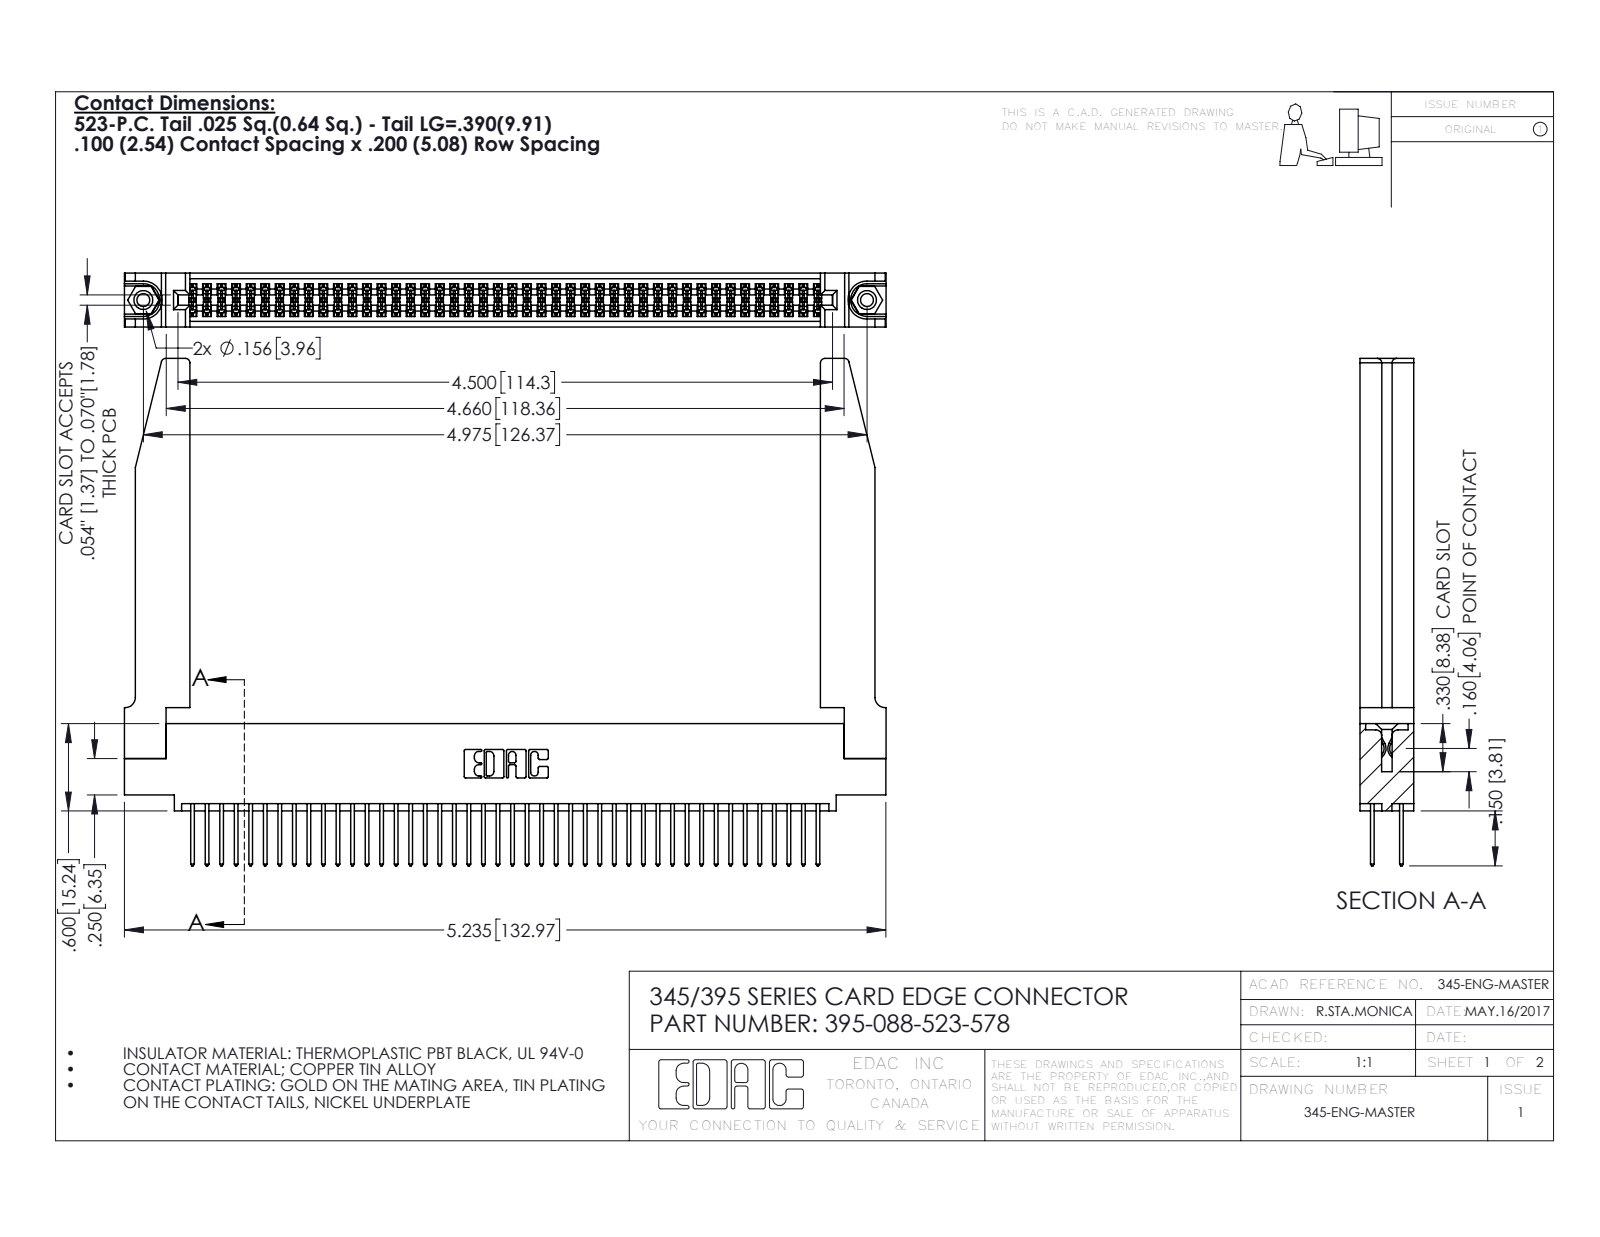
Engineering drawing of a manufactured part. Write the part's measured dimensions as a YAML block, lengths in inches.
part_name: "345-250-001_345-250-001-102; 345-220-078_345-220-078; 345-292-001_345-293-123; 345 Part_0.110 Offset - 0.156 Dia-TH (+1 more)"
step_written_by: "SolidWorks 2016 (CONFIG_CONTROL_DESIGN)"
units: inches
bodies: {solids: 93, faces: 4764, planar: 3130, cylindrical: 1582, other: 52}
overall_size: [5.236, 3.487, 0.37]
volume: 1.27
surface_area: 41.95
round_holes:
  - {diameter: 0.089, count: 2}
  - {diameter: 0.125, count: 2}
  - {diameter: 0.156, count: 2}
  - {diameter: 0.064, count: 1}
round_bosses_or_shafts:
  - {diameter: 0.155, count: 2}
partial_cylinders:
  - {radius: 0.006, count: 132}
  - {radius: 0.01, count: 88}
  - {radius: 0.01, count: 22}
  - {radius: 0.03, count: 8}
  - {radius: 0.007, count: 6}
  - {radius: 0.031, count: 6}
  - {radius: 0.026, count: 3}
  - {radius: 0.014, count: 2}
face_to_face_distances: [0.072, 0.298, 0.37, 0.2, 0.098, 0.272, 0.025, 0.225, 0.175, 0.148]
hole_center_spacings: [0.27, 4.739, 4.975]
